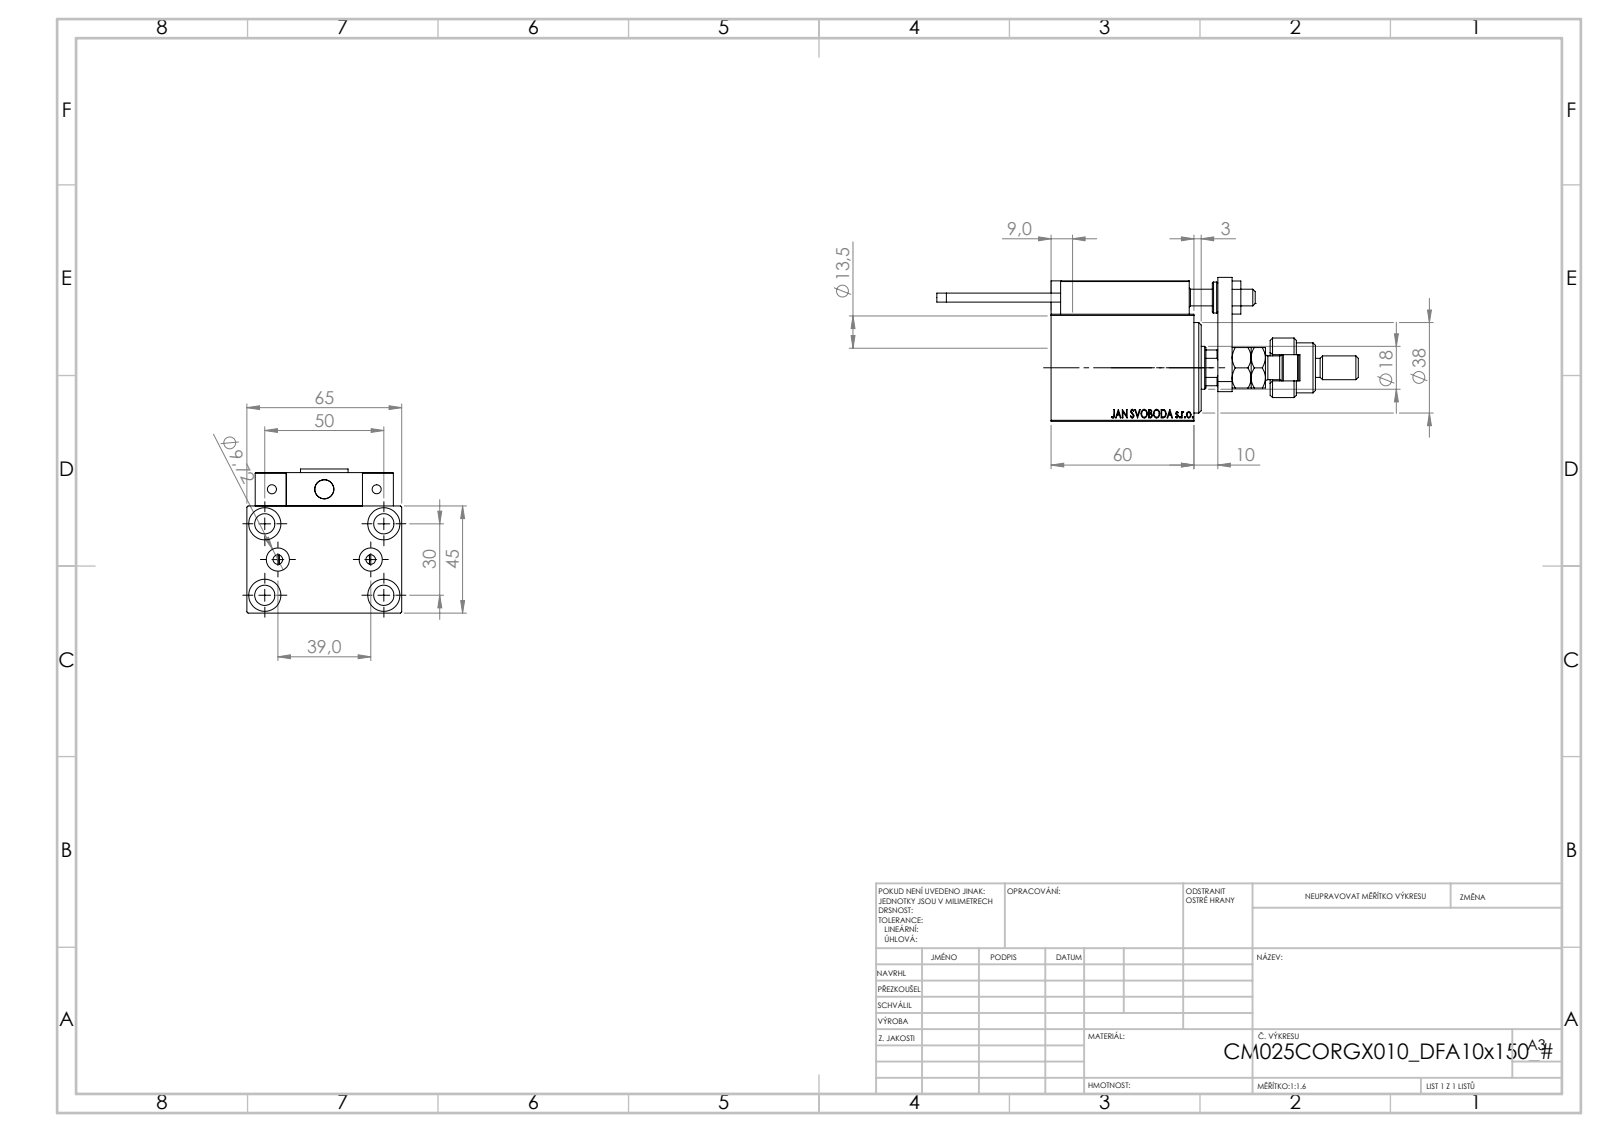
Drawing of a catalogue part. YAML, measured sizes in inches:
part_name: "V450CM_C_VCP; SWITCH_X_FRONT_BACK; V450CM_VC_B; NUT_D12 (+7 more)"
step_written_by: "SolidWorks 2019 (CONFIG_CONTROL_DESIGN)"
units: inches
bodies: {solids: 25, faces: 1363, planar: 588, cylindrical: 197, other: 578}
overall_size: [7.008, 2.559, 2.382]
volume: 12.87
surface_area: 103.5
round_holes:
  - {diameter: 0.157, count: 6}
  - {diameter: 0.315, count: 5}
  - {diameter: 0.335, count: 5}
  - {diameter: 0.126, count: 4}
  - {diameter: 0.531, count: 4}
  - {diameter: 0.197, count: 2}
  - {diameter: 0.383, count: 2}
  - {diameter: 0.276, count: 1}
  - {diameter: 0.571, count: 1}
  - {diameter: 0.709, count: 1}
  - {diameter: 0.846, count: 1}
  - {diameter: 1.063, count: 1}
round_bosses_or_shafts:
  - {diameter: 0.197, count: 2}
  - {diameter: 0.15, count: 2}
  - {diameter: 0.984, count: 1}
  - {diameter: 0.827, count: 1}
  - {diameter: 0.63, count: 1}
  - {diameter: 0.512, count: 1}
  - {diameter: 0.433, count: 1}
  - {diameter: 0.394, count: 1}
partial_cylinders:
  - {radius: 0.012, count: 30}
  - {radius: 0.118, count: 2}
  - {radius: 0.217, count: 1}
  - {radius: 0.335, count: 1}
  - {radius: 0.344, count: 1}
face_to_face_distances: [1.772, 0.551, 2.559, 2.323, 0.197, 0.118, 0.512, 0.236, 0.394, 0.315]
hole_center_spacings: [0.629, 1.148, 1.849, 0.448, 0.479, 0.768, 0.787, 0.987]
